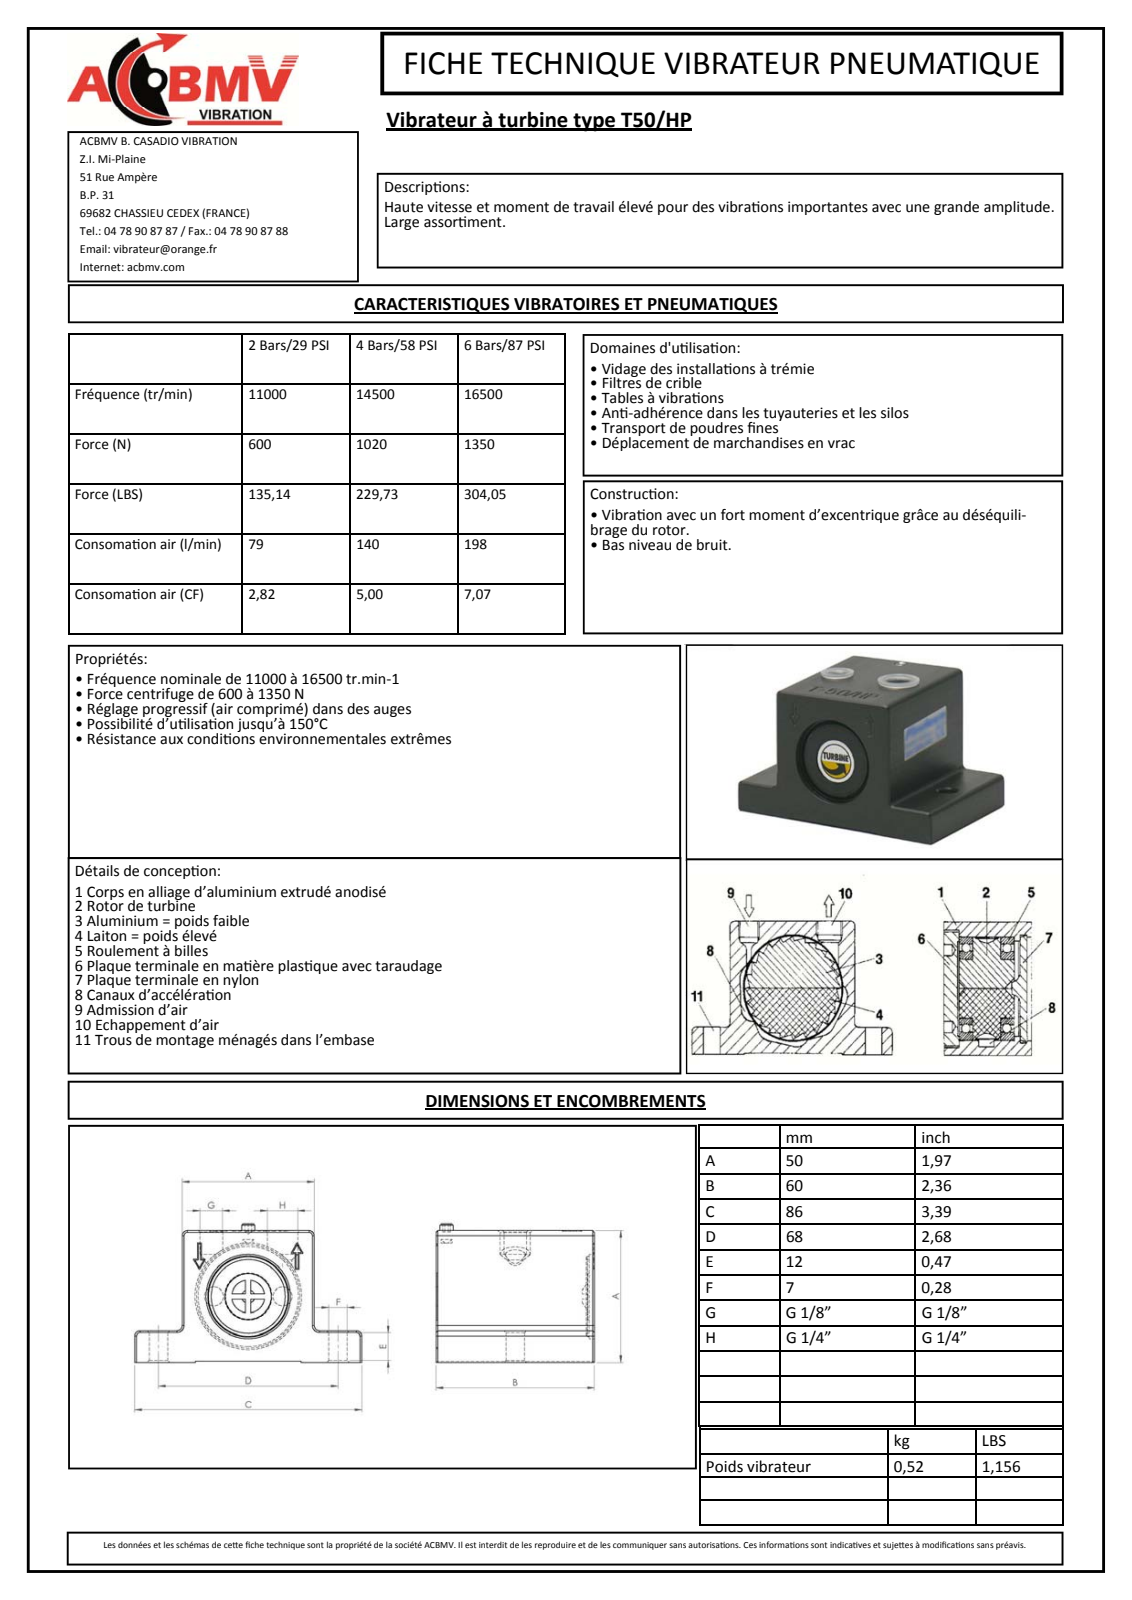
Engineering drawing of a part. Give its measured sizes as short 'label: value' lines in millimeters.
name: 8050-20-M
written by: Autodesk Inventor 2011 (CONFIG_CONTROL_DESIGN)
unit: mm
bodies: 1 solid, 361 faces (227 planar, 94 cylindrical, 40 other)
size: 86 × 60 × 52.5
volume: 169 878 mm³; area: 23 420 mm²
holes: 2× ⌀7, 2× ⌀7.2, 1× ⌀1.79, 1× ⌀4.13, 1× ⌀8.57, 1× ⌀11.45, 1× ⌀17.5, 1× ⌀18, 1× ⌀32
bosses: 1× ⌀28, 1× ⌀5, 1× ⌀1.61
rounds: 17× R0.25, 14× R0.2, 6× R1.25, 6× R2, 4× R0.46, 4× R1.75, 3× R0.31, 3× R0.54
face distances: 50, 0.5, 49.5, 60, 12, 11.5, 38, 18, 68, 86
hole spacings: 13, 42.8, 15.85, 16.68, 20, 21, 26, 26.12
